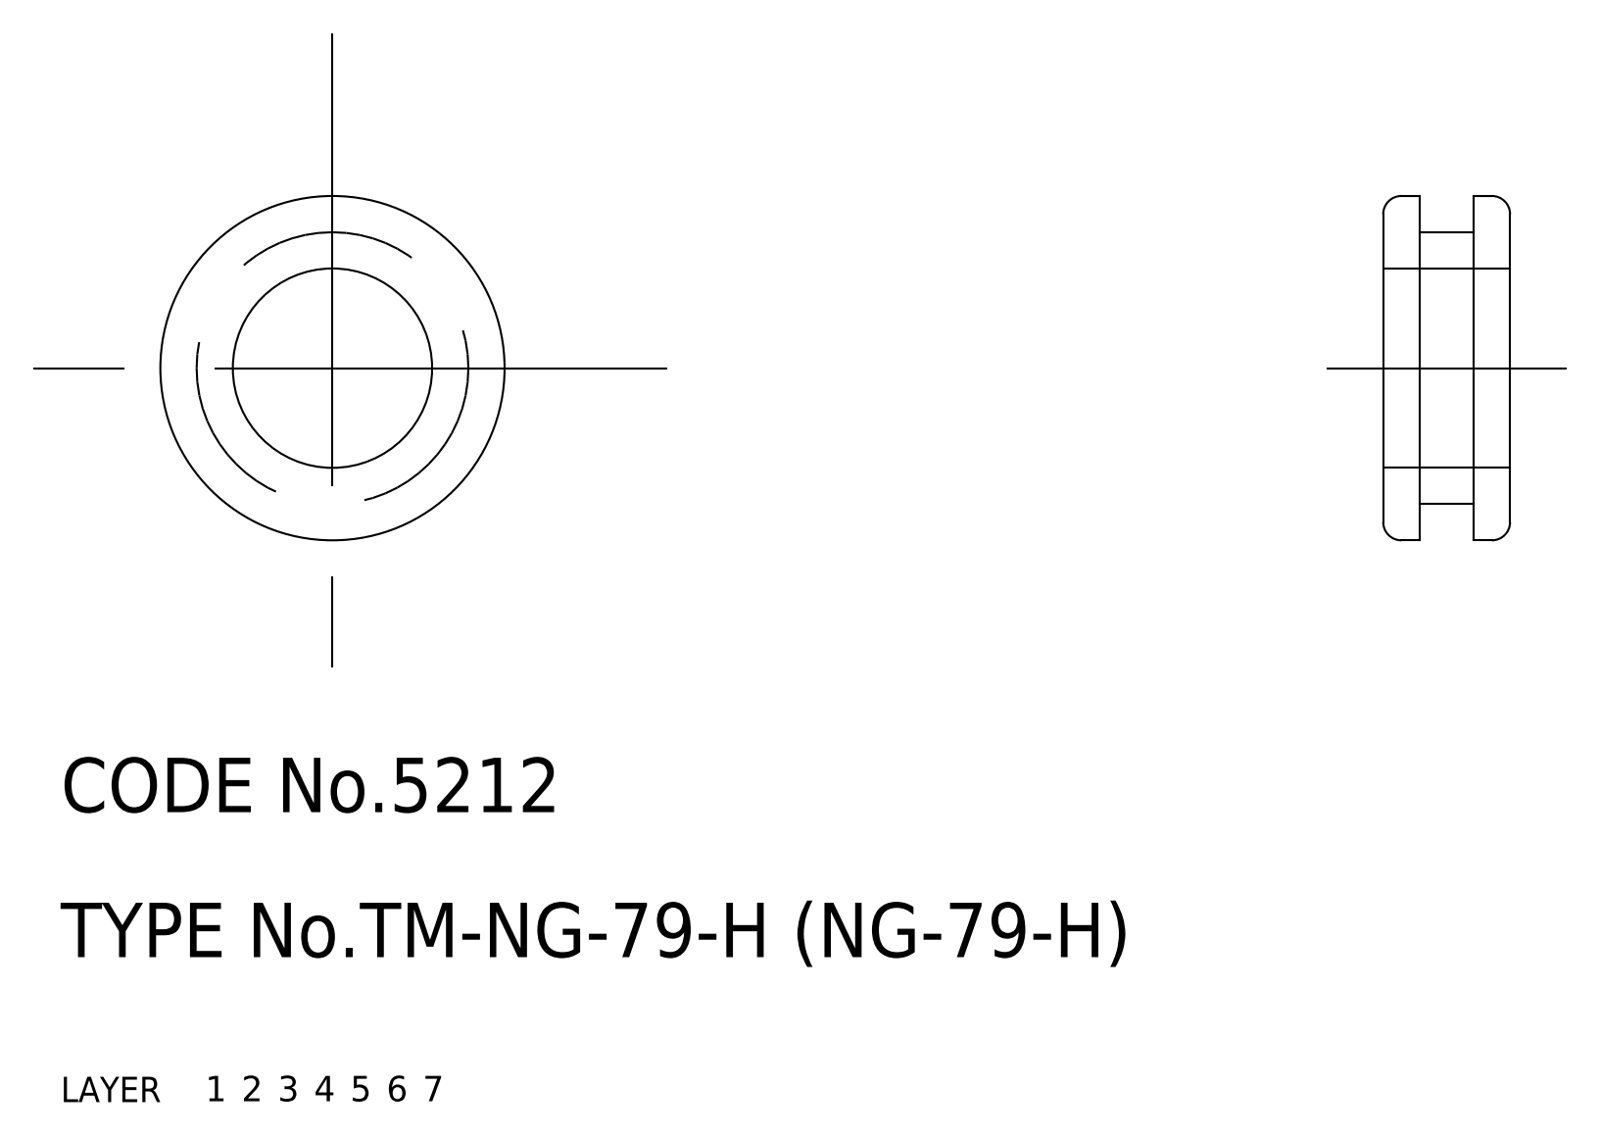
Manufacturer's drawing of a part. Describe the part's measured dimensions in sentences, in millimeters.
The part is named "grommet". Its 3-D file was written by "CADfix (AUTOMOTIVE_DESIGN)". It is 1 solid with 16 faces: 0 planar, 0 cylindrical and 16 other. Overall it measures 19 by 19 by 7 millimeters. Its volume is 976 cubic millimeters and its surface area 1 161 square millimeters.
